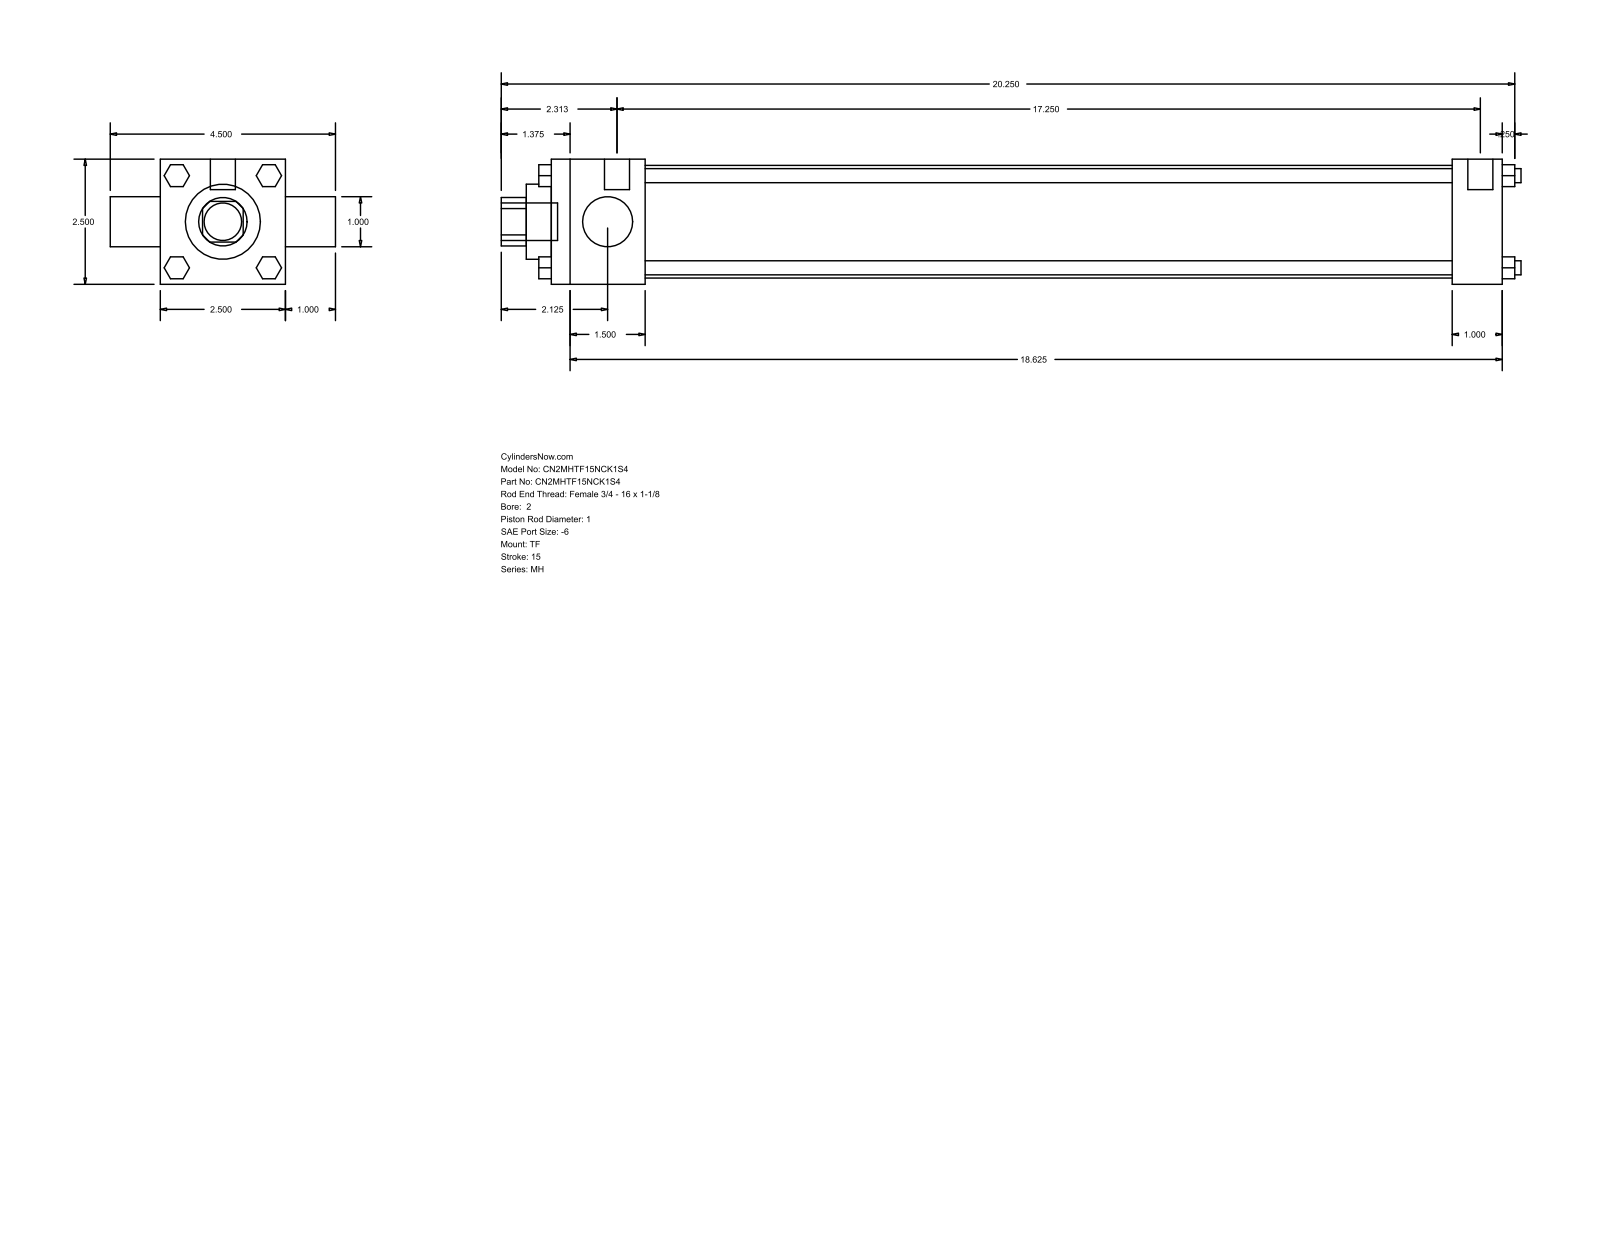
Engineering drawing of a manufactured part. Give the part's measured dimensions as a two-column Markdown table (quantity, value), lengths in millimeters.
| quantity | value |
| --- | --- |
| part name | MH_TF__0200_1 |
| STEP written by | GSSL Pune (CONFIG_CONTROL_DESIGN) |
| units | millimeters |
| bodies | 0 solids, 120 faces (92 planar, 28 cylindrical, 0 other) |
| overall size | 517.52 × 114.3 × 63.5 |
| round holes (diameter × count) | 25.4 × 2, 38.1 × 1, 57.15 × 1 |
| round bosses / shafts (diameter × count) | 7.14 × 4, 5.56 × 3, 12.7 × 2, 19.05 × 1 |
| partial cylindrical surfaces (radius × count) | 12.29 × 1 |
| main face-to-face distances | 63.5, 482.6, 25.4, 47.63, 457.2, 409.57, 434.97, 88.9, 495.3, 6.35 |
